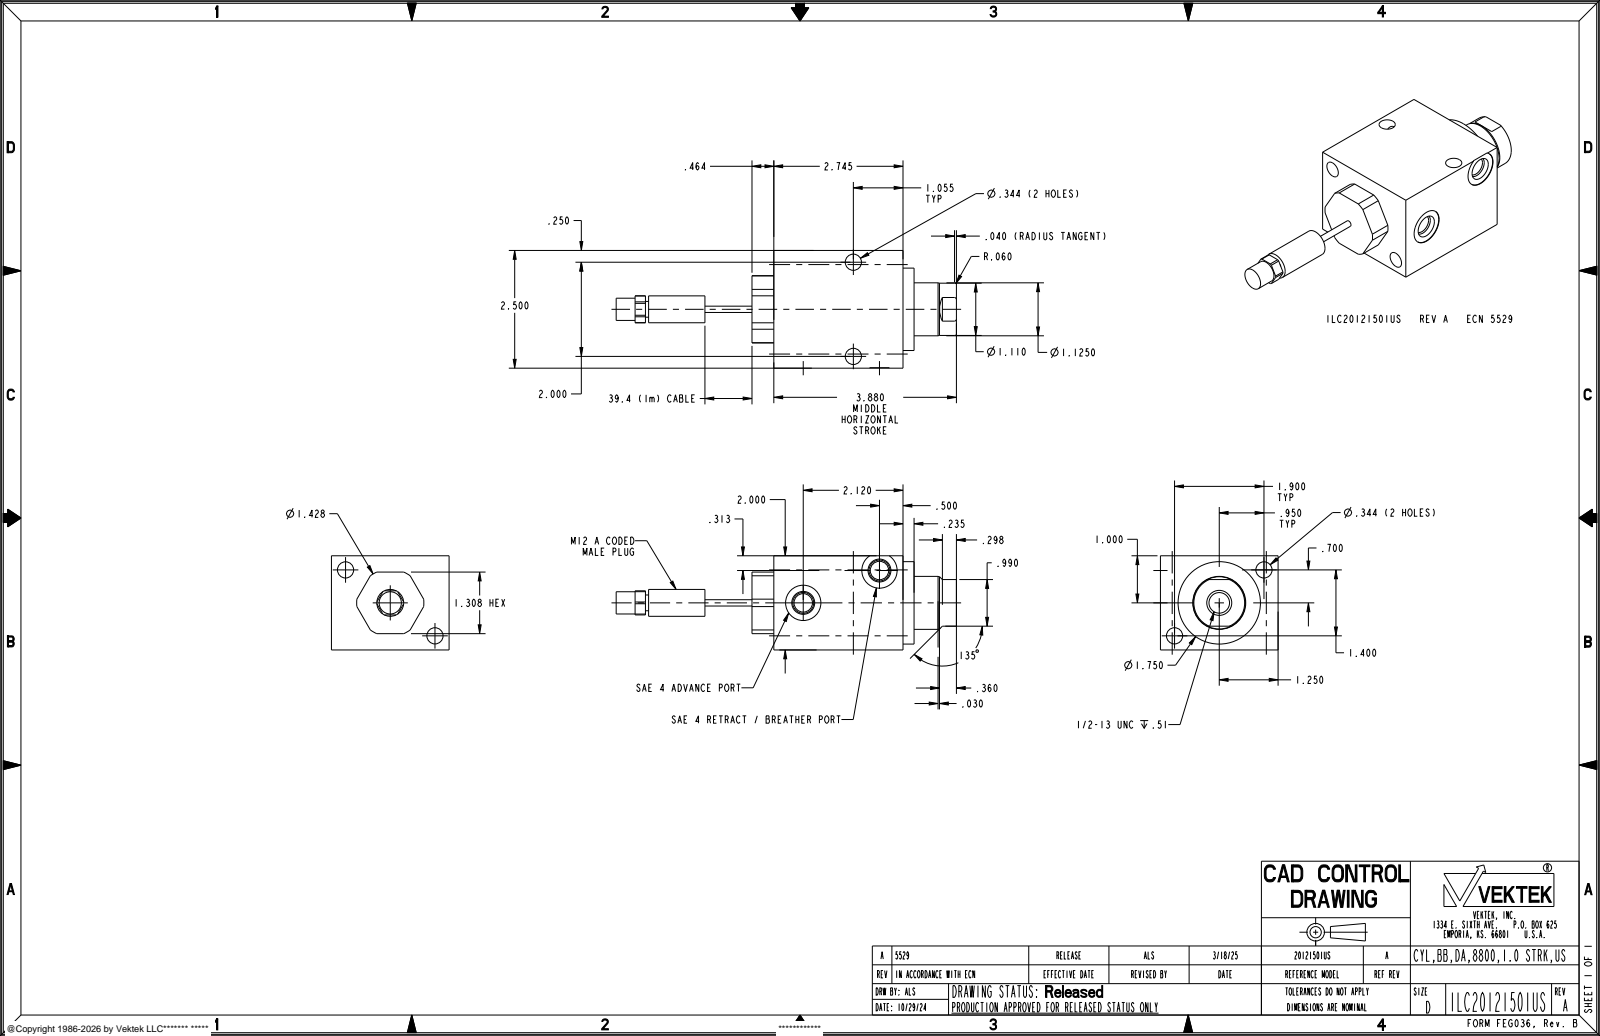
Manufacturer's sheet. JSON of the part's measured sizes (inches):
{"part_name": "ILC20121501US", "step_written_by": "CREO PARAMETRIC BY PTC INC, 2021164 (AUTOMOTIVE_DESIGN)", "units": "inches", "bodies": {"solids": 1, "faces": 99, "planar": 36, "cylindrical": 49, "other": 14}, "overall_size": [7.23, 2.75, 2], "volume_in3": 15.2, "surface_area_in2": 57.11, "round_holes": [[0.344, 4], [0.392, 2], [0.75, 2], [0.437, 1]], "round_bosses_or_shafts": [[1.75, 1], [1.125, 1], [1.11, 1], [0.571, 1], [0.5, 1], [0.472, 1], [0.335, 1], [0.134, 1]], "partial_cylinders_radius": [[0.714, 1]], "face_to_face_distances": [2, 2.5, 2.745, 3.209, 0.464, 0.235, 2.98, 3.444, 1.308, 0.9], "hole_center_spacings": [1.18, 1.76, 2, 2.36]}
